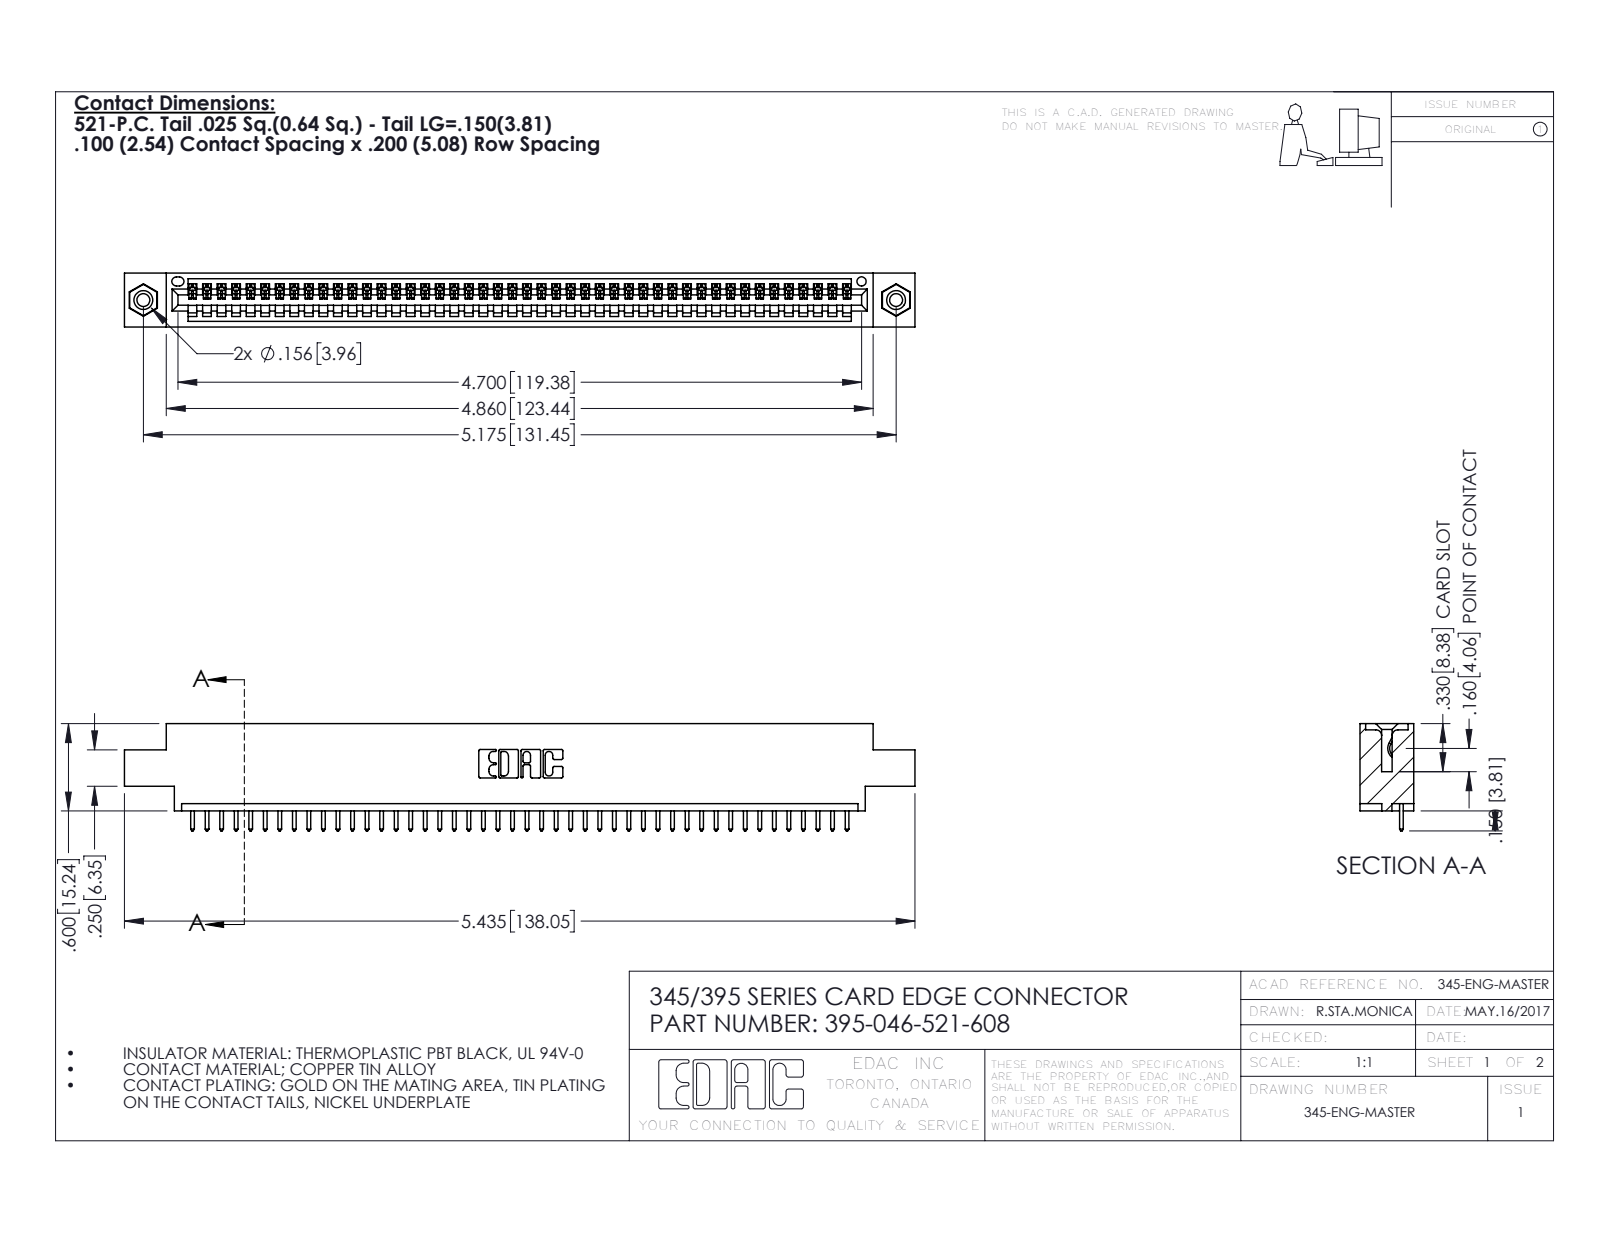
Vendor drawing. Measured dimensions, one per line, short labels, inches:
name: 345 Part_0.170 Offset - 0.156 Dia-TI; 395-046-521-608; 345-292-001_345-293-121; 345-250-001_345-250-003-102
written by: SolidWorks 2016 (CONFIG_CONTROL_DESIGN)
unit: in
bodies: 49 solids, 2858 faces (1956 planar, 886 cylindrical, 16 other)
size: 5.435 × 0.737 × 0.37
volume: 0.787 in³; area: 26.08 in²
holes: 2× ⌀0.089, 2× ⌀0.125, 2× ⌀0.156, 1× ⌀0.064
bosses: 2× ⌀0.155
rounds: 92× R0.006, 92× R0.01, 22× R0.01, 6× R0.007, 6× R0.031, 3× R0.026, 2× R0.031, 2× R0.04
face distances: 0.072, 0.298, 0.37, 0.2, 0.098, 0.272, 0.025, 0.225, 0.175, 0.149
hole spacings: 0.27, 4.939, 5.175
